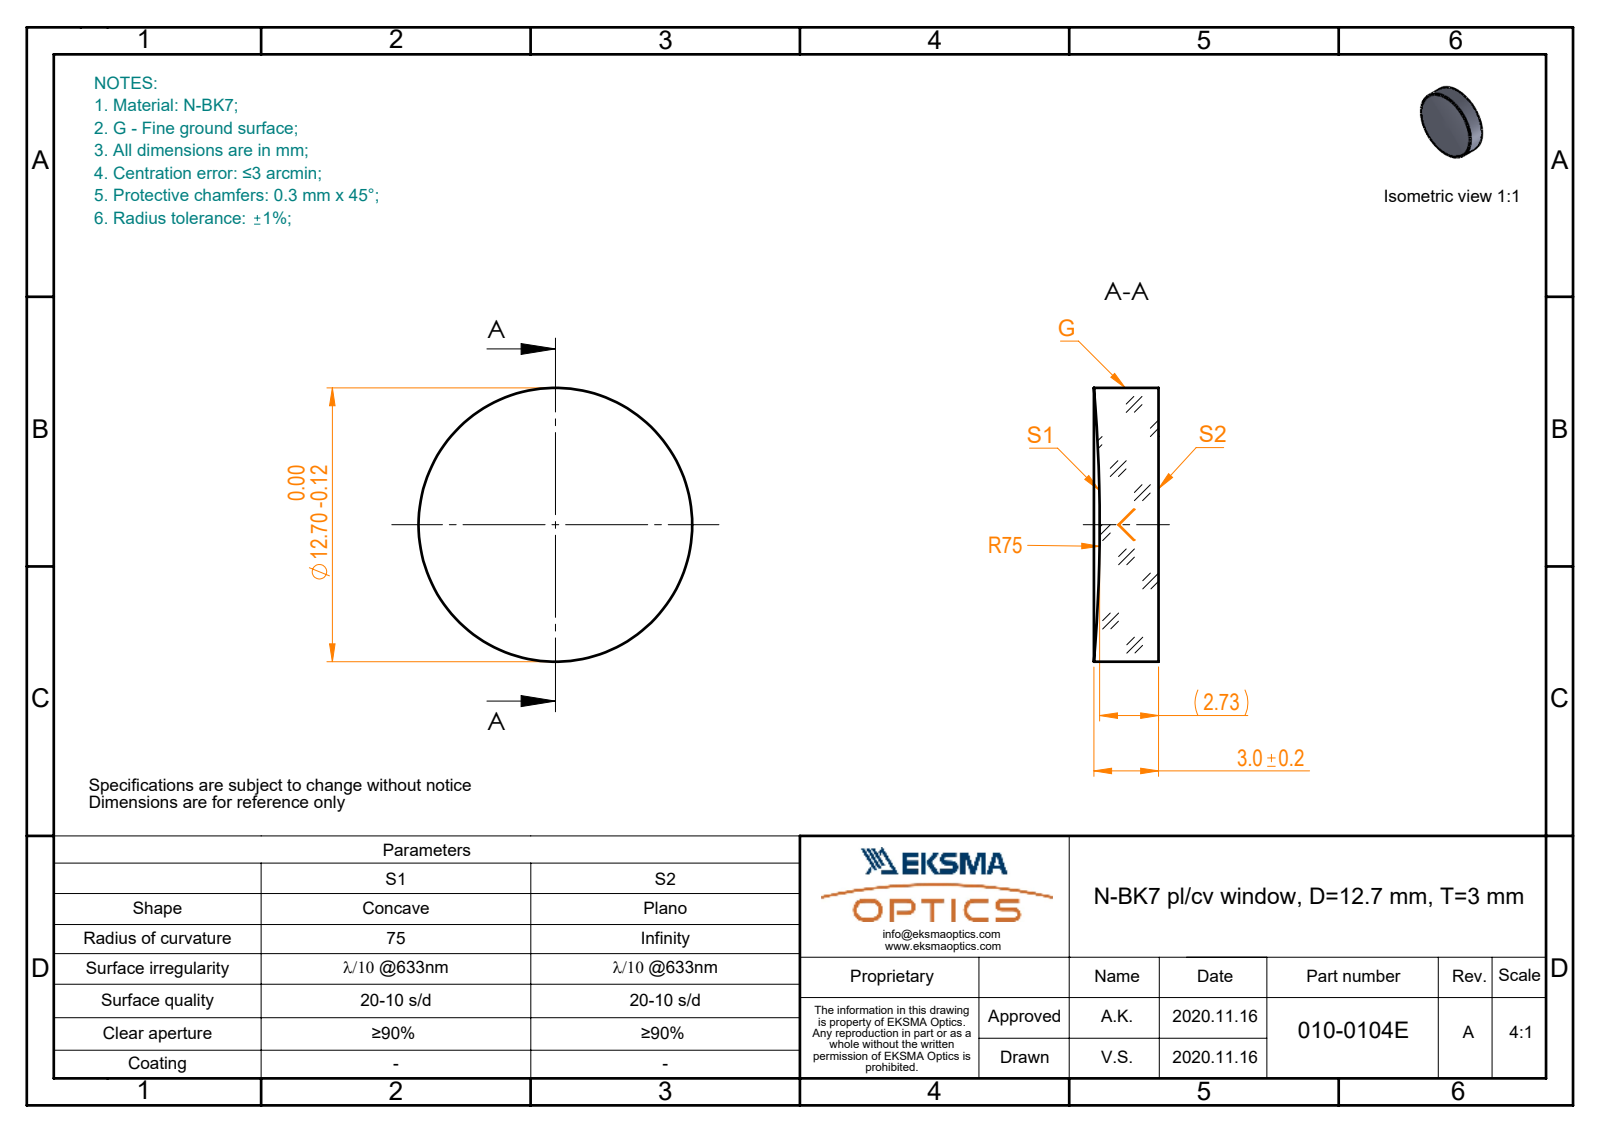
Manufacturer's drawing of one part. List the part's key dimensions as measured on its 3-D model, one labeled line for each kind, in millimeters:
Part name (STEP PRODUCT): 010-0104E_N-BK7_PCV_window
STEP written by: SolidWorks 2019 (CONFIG_CONTROL_DESIGN)
Units: millimetres
Bodies: 1 solid, 5 faces (1 planar, 2 cylindrical, 2 other)
Overall size (bounding box): 12.7 × 12.7 × 3
Volume: 363 mm³ · Surface area: 373 mm²
Round bosses / shafts (diameter × count): ⌀12.7 ×1
